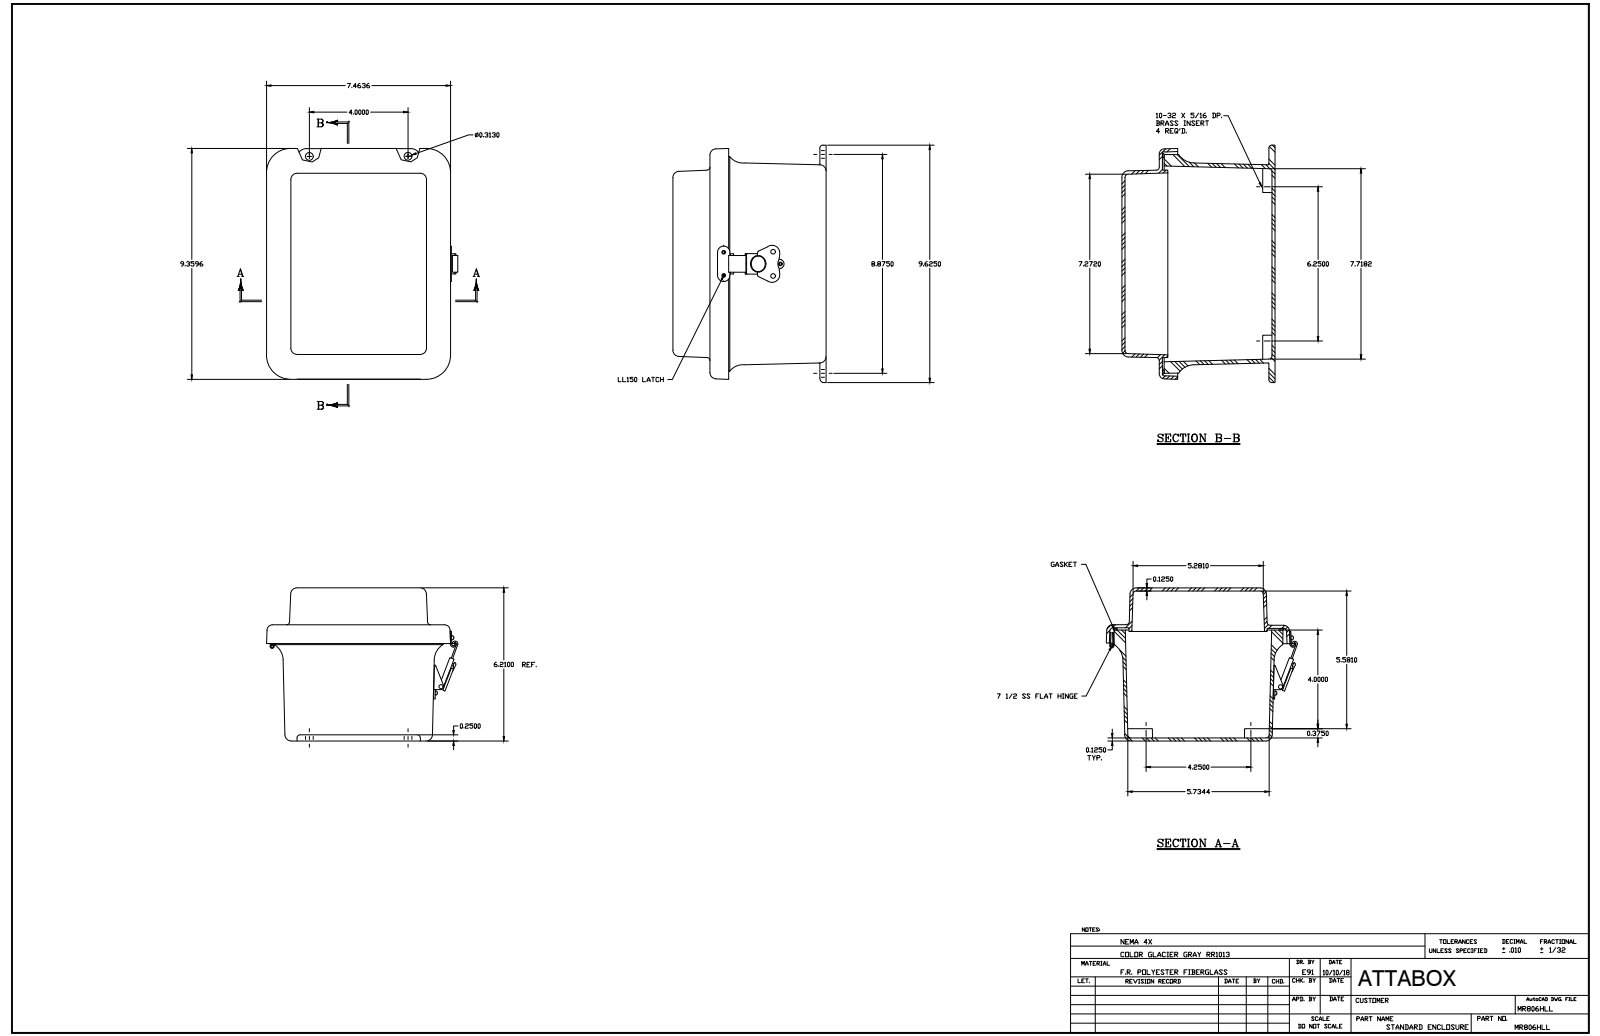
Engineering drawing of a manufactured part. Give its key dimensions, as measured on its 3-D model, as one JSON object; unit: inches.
{"part_name": "MR806HLL", "step_written_by": "SolidWorks 2018 (AUTOMOTIVE_DESIGN)", "units": "inches", "bodies": {"solids": 30, "faces": 826, "planar": 344, "cylindrical": 308, "other": 174}, "overall_size": [9.625, 7.597, 6.215], "volume_in3": 48.67, "surface_area_in2": 688.2, "round_holes": [[0.14, 10], [0.131, 6], [0.152, 5], [0.156, 4], [0.218, 4], [0.13, 2], [0.165, 2], [0.197, 2], [0.085, 1], [0.085, 1], [0.106, 1], [0.118, 1]], "round_bosses_or_shafts": [[0.25, 9], [0.125, 6], [0.27, 4], [0.125, 3], [0.583, 1], [0.524, 1], [0.209, 1], [0.185, 1]], "partial_cylinders_radius": [[0.031, 20], [0.125, 20], [0.25, 12], [0.079, 10], [0.039, 4], [0.047, 4], [0.2, 4], [0.31, 4]], "face_to_face_distances": [0.125, 0.125, 1.515, 5.965, 4.45, 6.09, 6.215, 6.089, 4.575, 1.64], "hole_center_spacings": [3.5, 1.326, 5.271, 7.249, 8.864, 0.25, 3.25, 0.469]}
